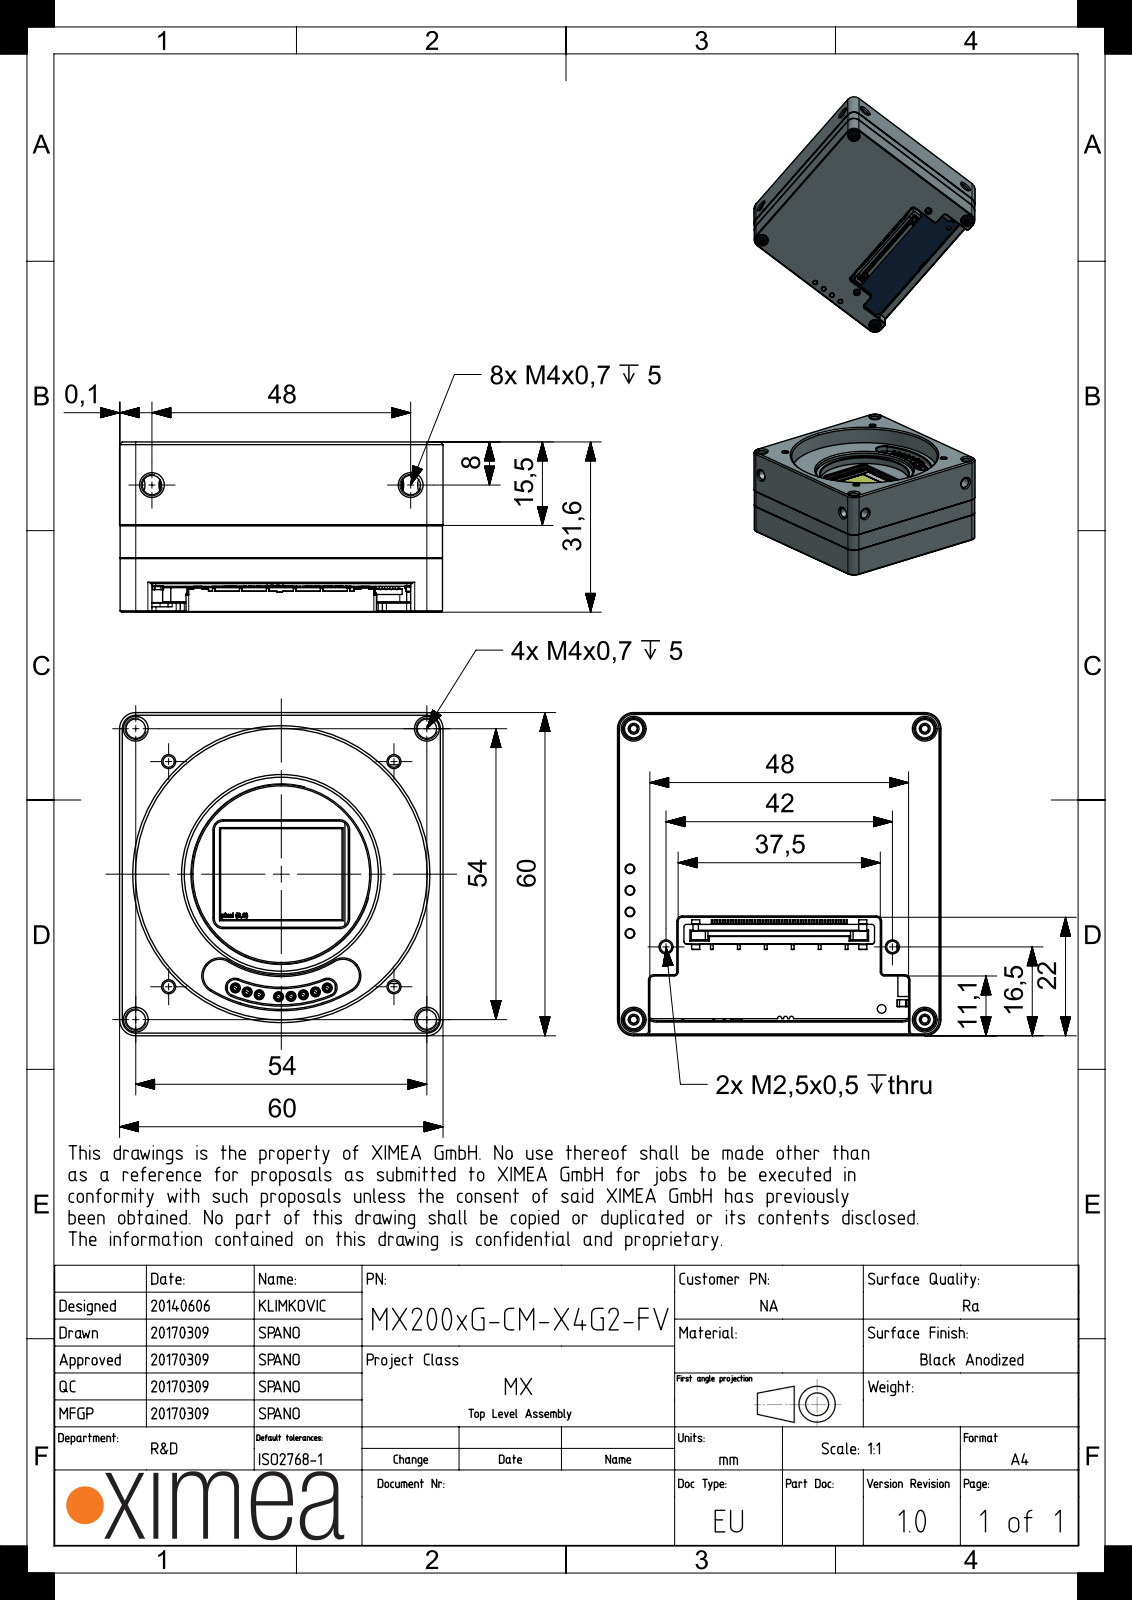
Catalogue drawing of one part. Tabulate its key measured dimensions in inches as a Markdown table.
| quantity | value |
| --- | --- |
| part name | MX-X4G2-MAIN-FV-LIGHTWEIGHT; MECH-GASKET-CB200; SROB-M2X20-IMBUS-STNLS; MECH-MX200-REAR (+8 more) |
| STEP written by | SIEMENS PLM Software NX 11.0 (AUTOMOTIVE_DESIGN) |
| units | inches |
| bodies | 42 solids, 3582 faces (1936 planar, 1017 cylindrical, 629 other) |
| overall size | 2.362 × 2.362 × 1.323 |
| volume | 3.194 in³ |
| surface area | 99.82 in² |
| round holes (diameter × count) | 0.063 × 20, 0.083 × 10, 0.051 × 9, 0.036 × 8, 0.043 × 8, 0.051 × 8, 0.142 × 8, 0.079 × 6, 0.028 × 4, 0.035 × 4, 0.043 × 4, 0.091 × 4 |
| round bosses / shafts (diameter × count) | 0.018 × 143, 0.072 × 8, 0.061 × 8, 0.059 × 8, 0.049 × 8, 0.042 × 8, 0.217 × 4, 0.15 × 4 |
| partial cylindrical surfaces (radius × count) | 0.059 × 70, 0.02 × 59, 0.118 × 35, 0.004 × 24, 0.008 × 18, 0.03 × 14, 0.197 × 12, 0.098 × 8 |
| main face-to-face distances | 0.039, 0.284, 0.352, 0.374, 0.324, 2.358, 0.035, 2.323, 0.244, 0.245 |
| hole center spacings | 1.901, 0.091, 0.34, 0.896, 0.896, 1.164, 1.503, 1.646 |
